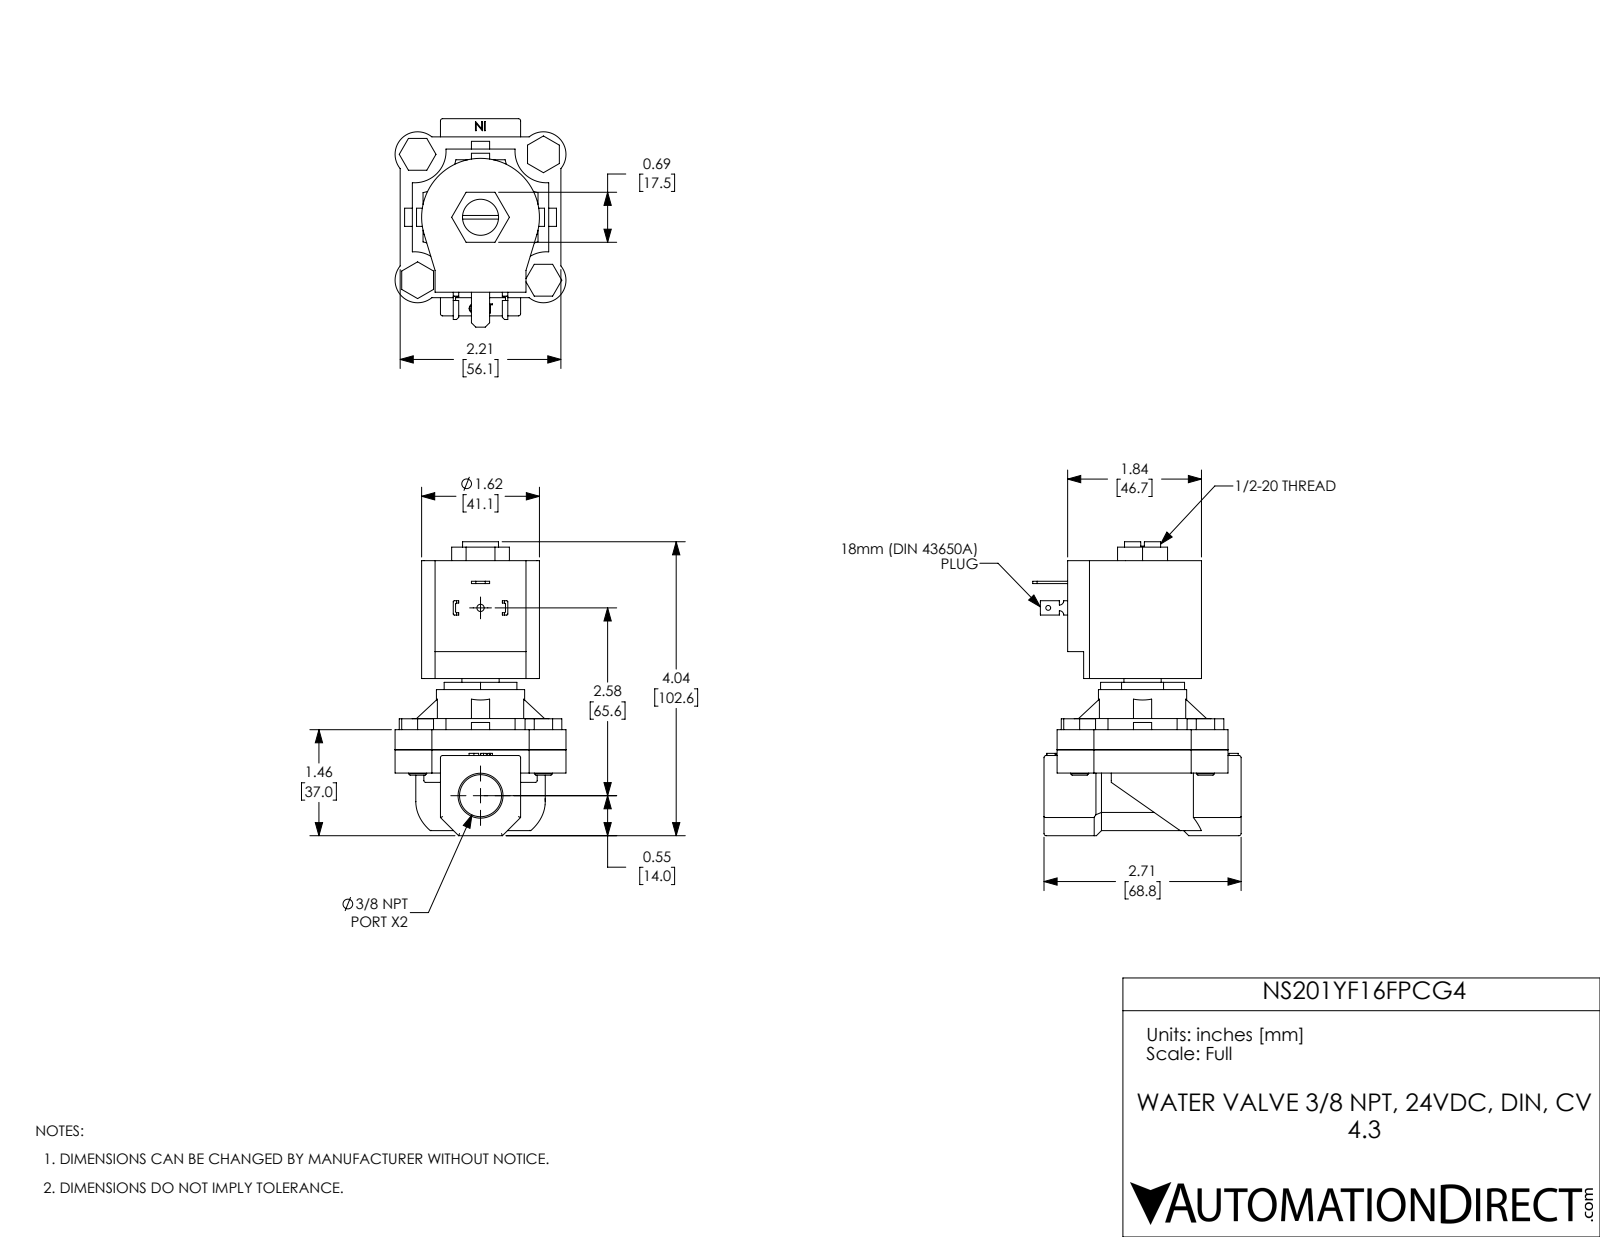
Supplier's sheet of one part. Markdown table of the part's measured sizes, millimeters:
| quantity | value |
| --- | --- |
| part name | NS201YF16FPCG4 |
| STEP written by | SolidWorks 2017 (AUTOMOTIVE_DESIGN) |
| units | millimeters |
| bodies | 11 solids, 383 faces (237 planar, 113 cylindrical, 33 other) |
| overall size | 102.6 × 72.8 × 59.7 |
| volume | 168 800 mm³ |
| surface area | 43 080 mm² |
| round holes (diameter × count) | 6.4 × 4, 1.7 × 1, 2.5 × 1, 12.6 × 1, 13 × 1, 14.7 × 1, 29.3 × 1 |
| round bosses / shafts (diameter × count) | 6.3 × 4, 30.8 × 1 |
| partial cylindrical surfaces (radius × count) | 0.8 × 15, 0.4 × 8, 7.9 × 4, 11 × 4, 14.7 × 4, 1.5 × 2, 20.6 × 1, 22.6 × 1 |
| main face-to-face distances | 7, 66, 59, 8.1, 15.1, 74.1, 14.1, 42.1, 6.4, 62.5 |
| hole center spacings | 31.1, 43.9, 62.1, 65.6 |
